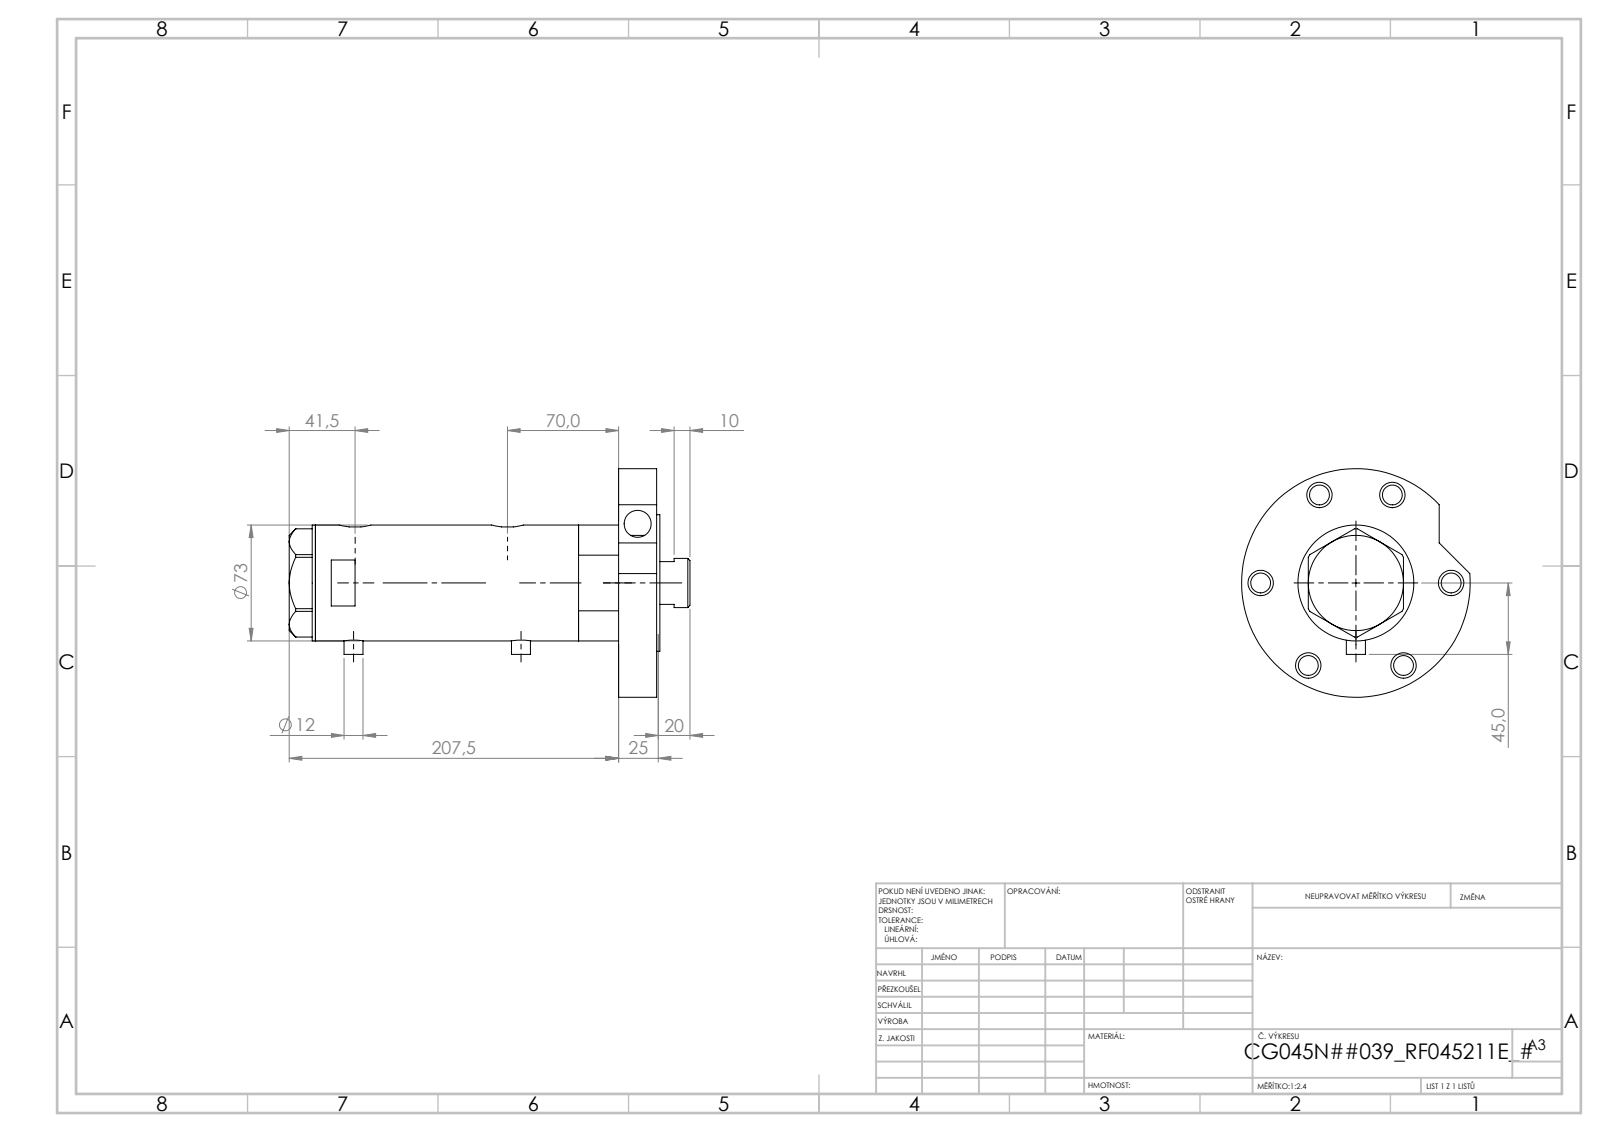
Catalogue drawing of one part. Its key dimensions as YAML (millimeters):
part_name: "V270CG_FRONT; V270CG_VC; V270CG_MIDDLE; V270CG_RF211E (+1 more)"
step_written_by: "SolidWorks 2019 (CONFIG_CONTROL_DESIGN)"
units: millimeters
bodies: {solids: 5, faces: 169, planar: 61, cylindrical: 88, other: 20}
overall_size: [230.52, 144, 144]
volume: 1073000
surface_area: 190829
round_holes:
  - {diameter: 12.5, count: 8}
  - {diameter: 16, count: 6}
  - {diameter: 5, count: 2}
  - {diameter: 13.16, count: 2}
  - {diameter: 10.5, count: 1}
  - {diameter: 17, count: 1}
  - {diameter: 32, count: 1}
  - {diameter: 33.5, count: 1}
  - {diameter: 45, count: 1}
  - {diameter: 48, count: 1}
  - {diameter: 60, count: 1}
  - {diameter: 64, count: 1}
round_bosses_or_shafts:
  - {diameter: 12, count: 2}
  - {diameter: 144, count: 1}
  - {diameter: 86, count: 1}
  - {diameter: 73, count: 1}
  - {diameter: 58, count: 1}
  - {diameter: 31, count: 1}
partial_cylinders:
  - {radius: 10, count: 2}
face_to_face_distances: [24, 26, 166.45, 2, 106.15, 140.45, 164.45, 192.45, 42.5, 182.95]
hole_center_spacings: [60, 66.67, 90.65, 99.77, 103.92, 107.62, 119.74, 0.99]
